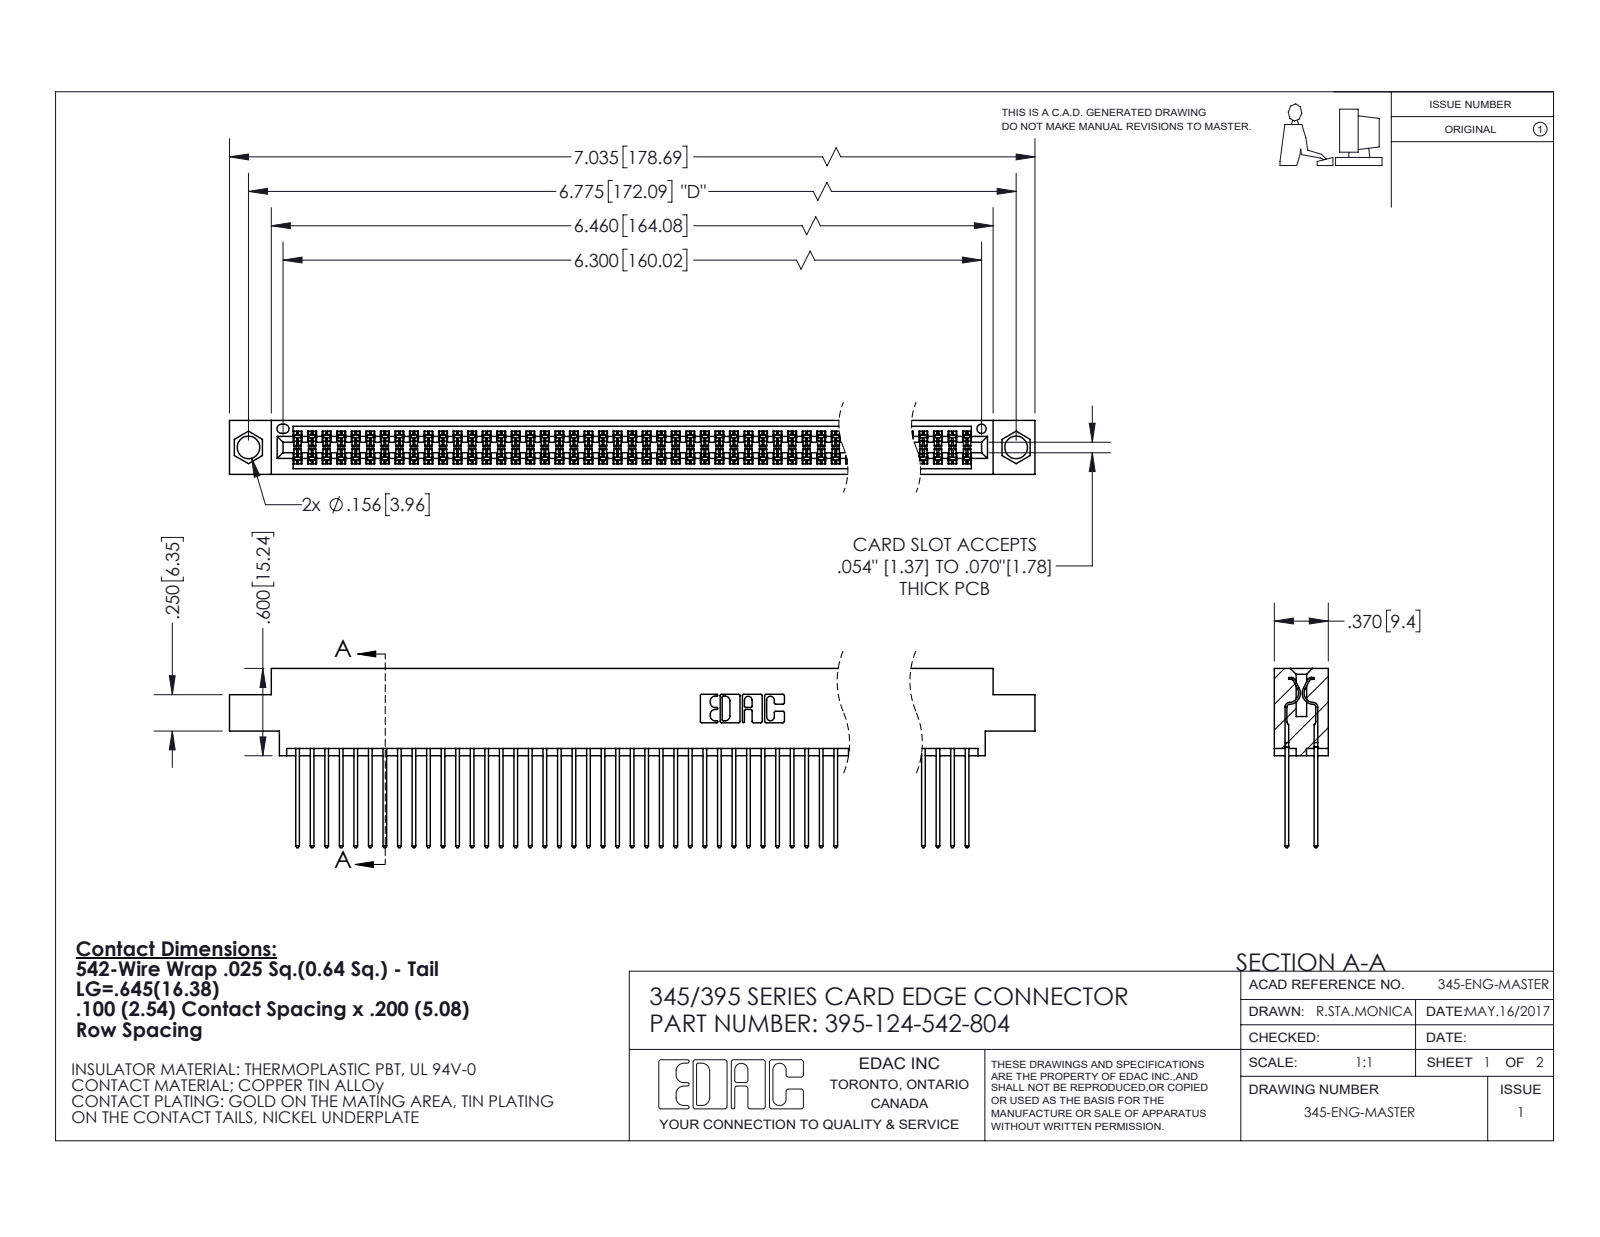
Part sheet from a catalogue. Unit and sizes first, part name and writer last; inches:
Units: inches
Overall size (bounding box): 7.035 × 1.232 × 0.37
Round holes (diameter × count): ⌀0.156 ×2, ⌀0.064 ×1
Partial cylindrical surfaces — rounded edges, fillets, slot ends (radius × count): R0.006 ×186, R0.01 ×124, R0.01 ×22, R0.007 ×6, R0.031 ×6, R0.026 ×3, R0.014 ×2, R0.019 ×2
Main face-to-face distances: 0.072, 0.298, 0.2, 0.098, 0.272, 0.025, 0.37, 0.225, 0.175, 0.149
Hole centre spacings: 0.27, 6.539, 6.775
Volume: 1.092 in³ · Surface area: 45.8 in²
Bodies: 125 solids, 6344 faces (4190 planar, 2154 cylindrical, 0 other)
Part name (STEP PRODUCT): 345-292-001_345-293-142; 345 Part_0.170 Offset - 0.156 Dia-TI; 395-124-542-804
STEP written by: SolidWorks 2020 (CONFIG_CONTROL_DESIGN)
